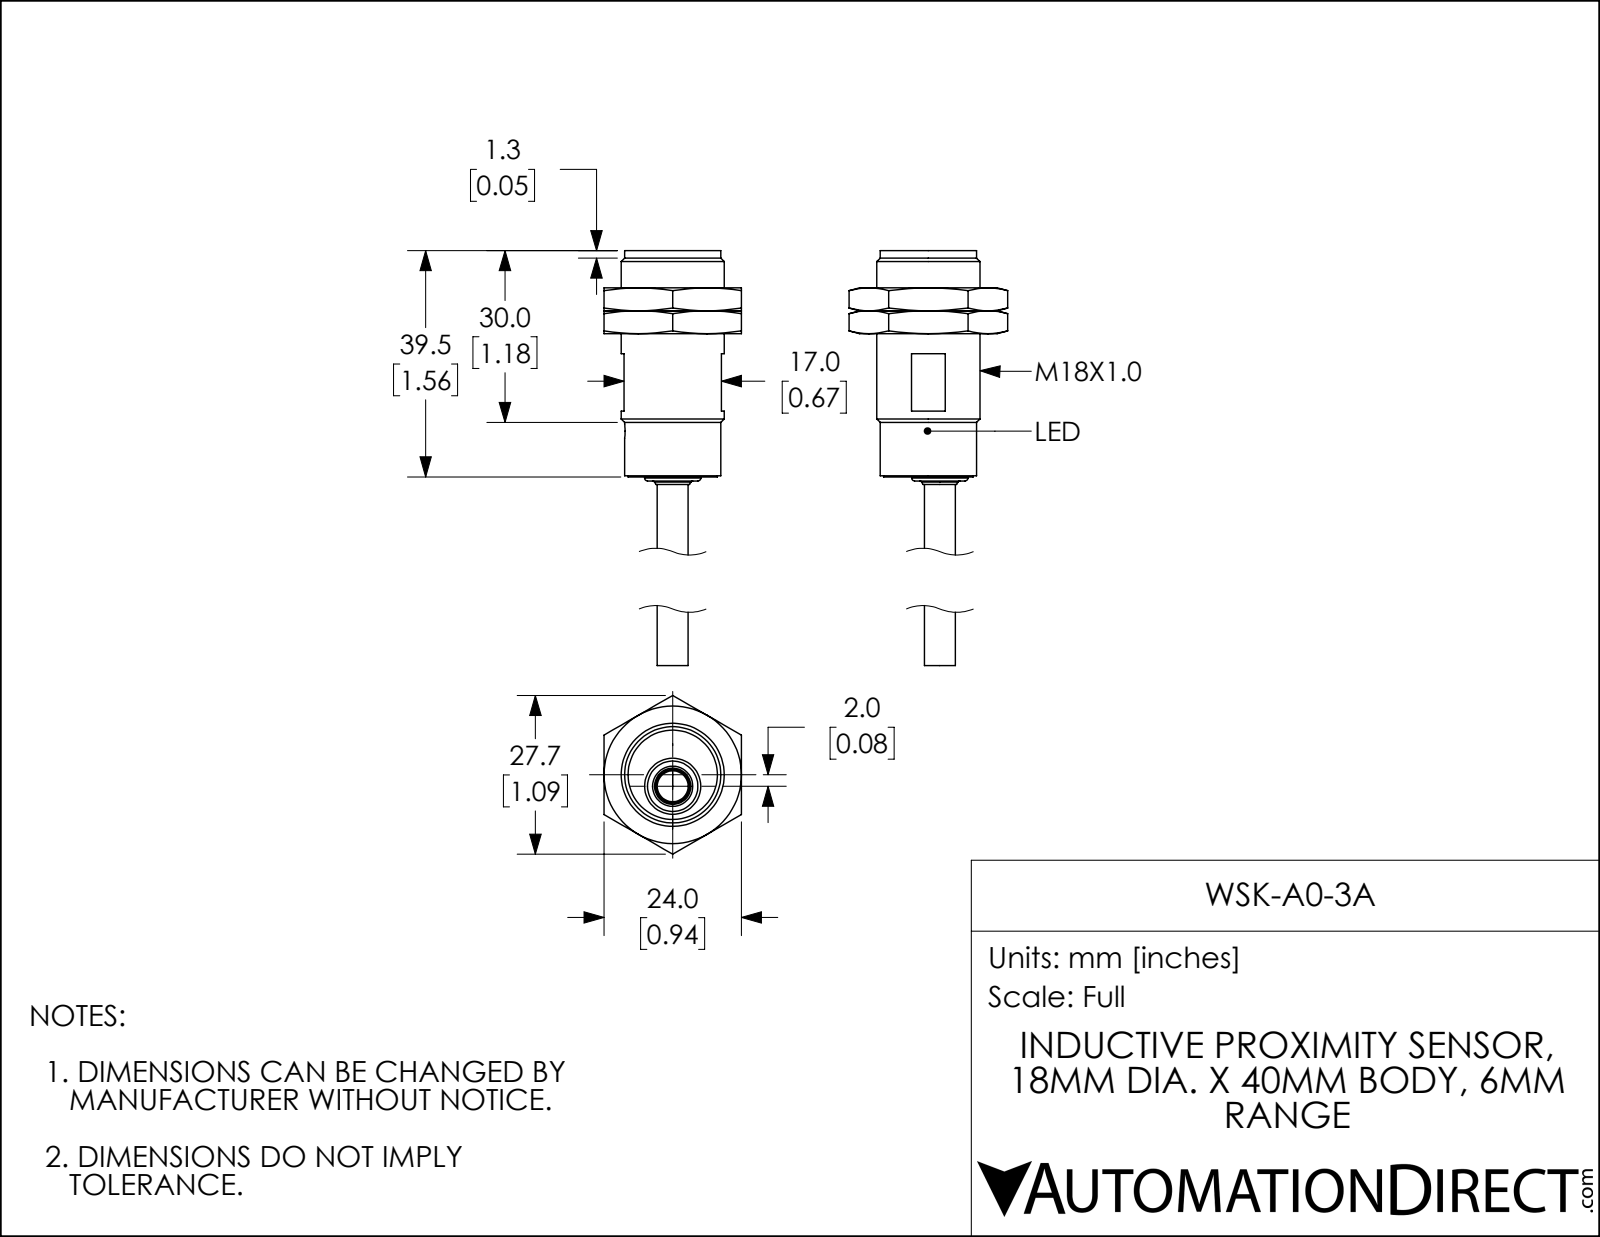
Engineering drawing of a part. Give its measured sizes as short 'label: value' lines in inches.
name: WSK-A0-3A
written by: SolidWorks 2017 (AUTOMOTIVE_DESIGN)
unit: in
bodies: 3 solids, 73 faces (31 planar, 9 cylindrical, 33 other)
size: 3.13 × 1.091 × 0.945
volume: 0.776 in³; area: 8.399 in²
holes: 1× ⌀0.098, 1× ⌀0.666
bosses: 1× ⌀0.709, 1× ⌀0.661, 1× ⌀0.614, 1× ⌀0.386, 1× ⌀0.213
face distances: 0.157, 0.945, 0.413, 0.256, 0.315, 0.571, 0.138, 0.807, 1.555, 0.984
